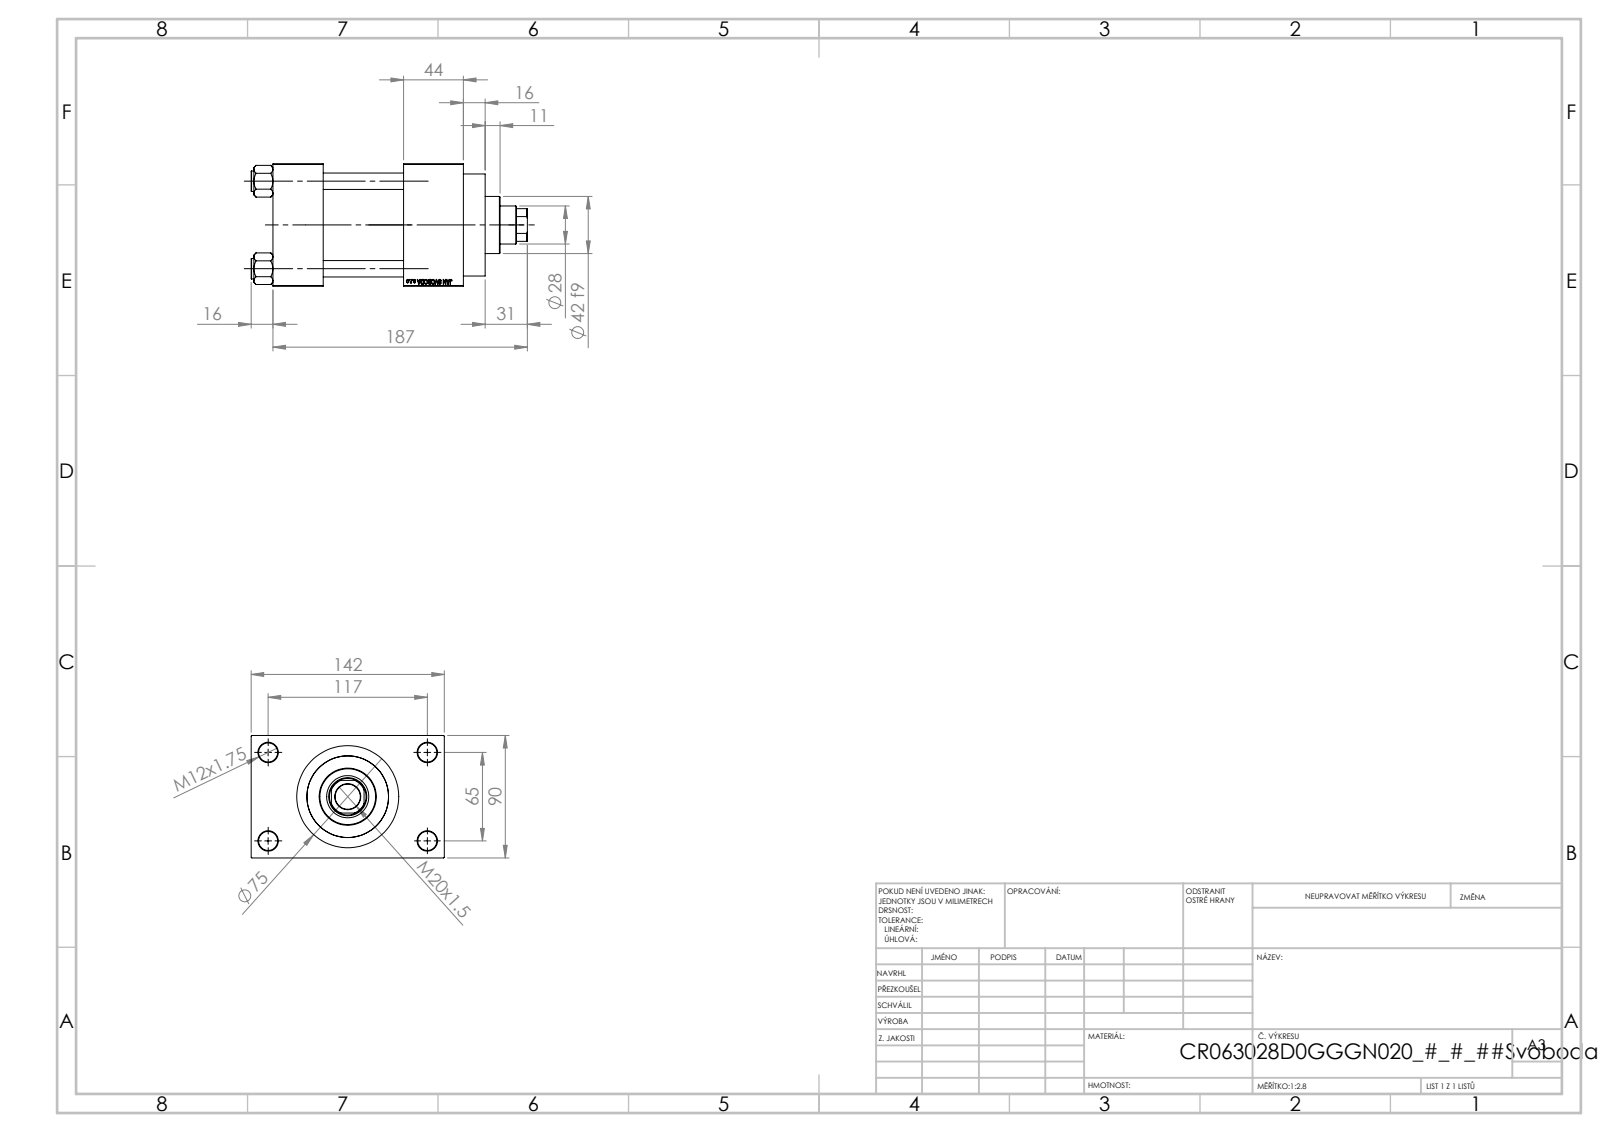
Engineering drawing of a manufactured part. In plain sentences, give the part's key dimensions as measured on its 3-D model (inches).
The part is named "NUT_M5_D; V215CR_D_TYCINKA; V215CR_D_Body; V215CR_VCP_D (+1 more)". Its 3-D file was written by "SolidWorks 2019 (CONFIG_CONTROL_DESIGN)". It is 11 solids with 1104 faces: 497 planar, 89 cylindrical and 518 other. Overall it measures 7.992 by 5.591 by 3.543 inches. Its volume is 67.43 cubic inches and its surface area 307.8 square inches. Round holes: 4 of diameter 0.472, 4 of diameter 0.551, 2 of diameter 0.276, 2 of diameter 0.825, 2 of diameter 1.181, 1 of diameter 0.728, 1 of diameter 1.102, 1 of diameter 1.22, 1 of diameter 1.969, 1 of diameter 2.362, 1 of diameter 2.48. Round bosses or shafts: 4 of diameter 0.591, 1 of diameter 2.953, 1 of diameter 2.717, 1 of diameter 1.654. Partial cylindrical surfaces (rounded edges, fillets, slot ends): 1 of radius 0.531. The main face-to-face distances are 3.543, 2.323, 1.457, 3.78, 5.512, 4.055, 1.732, 1.024, 4.567, 5.591. The hole center spacings are 1.037, 1.79, 2.531, 2.635, 2.748, 3.569, 4.383, 2.559.
